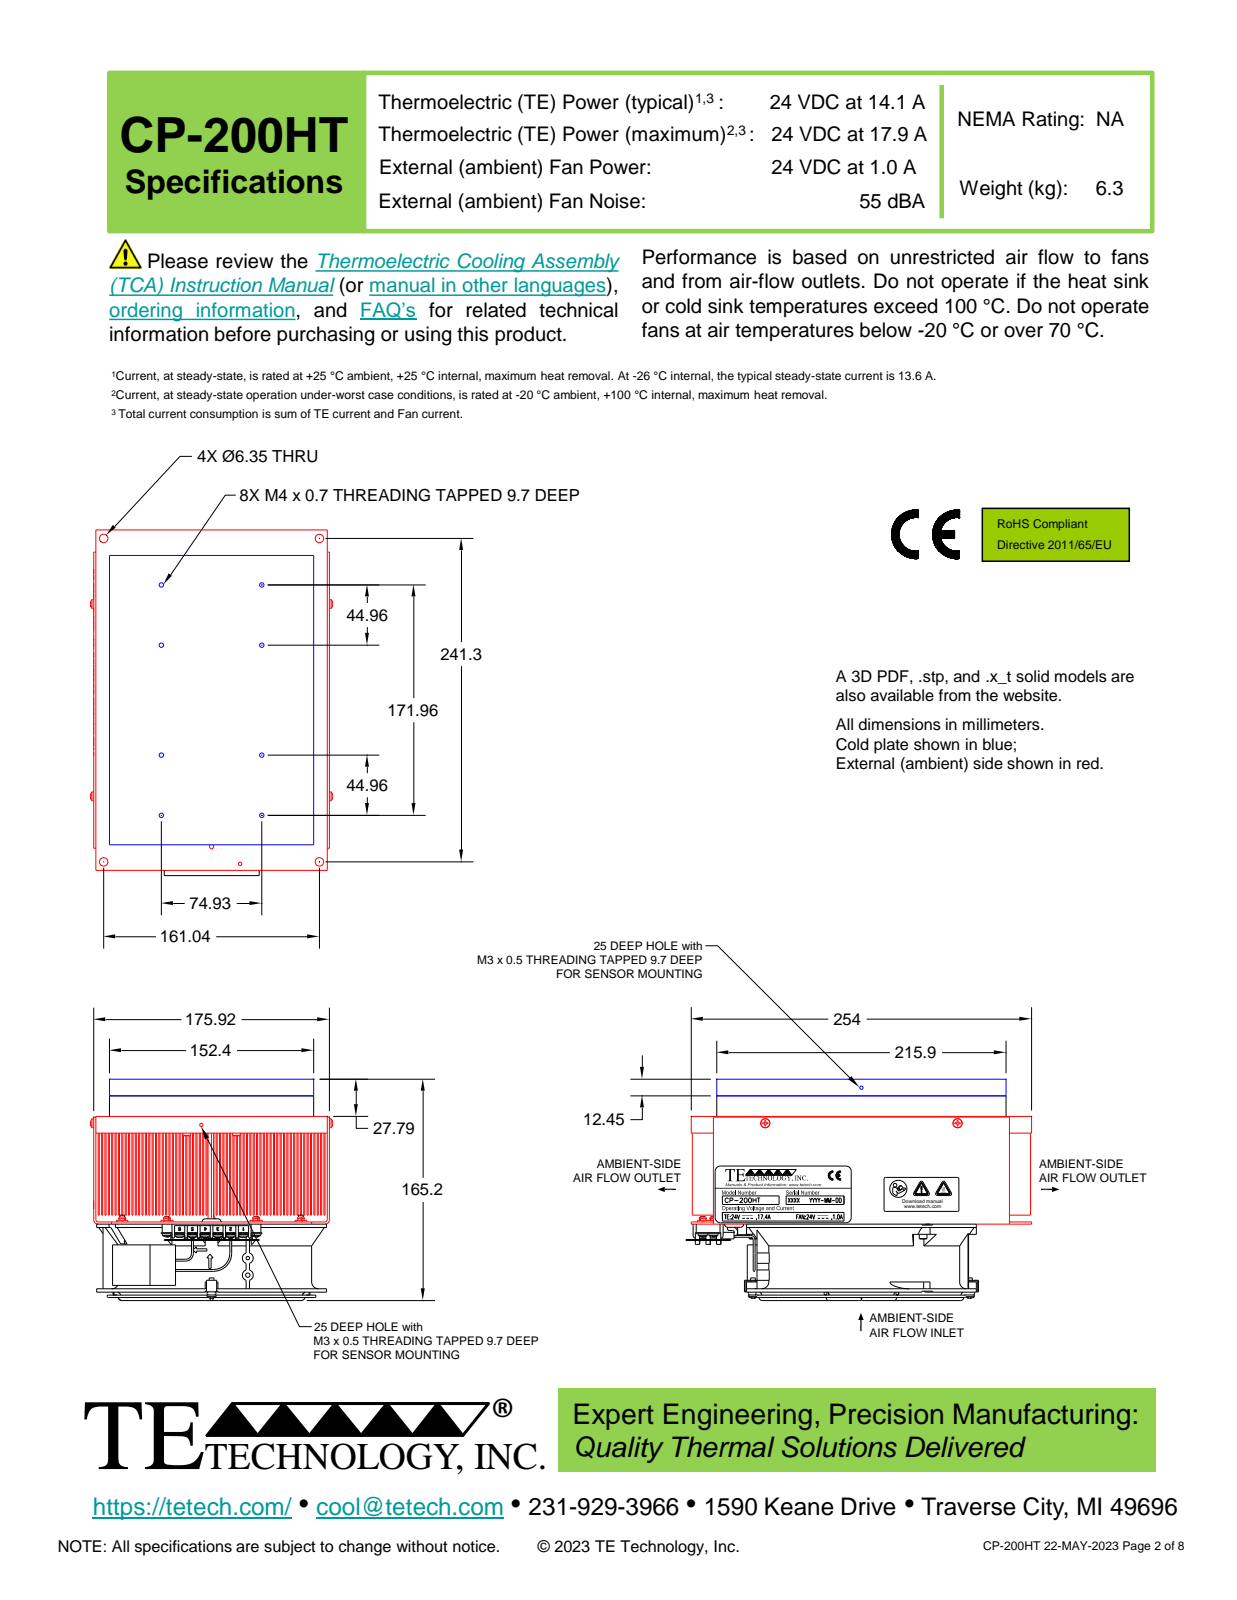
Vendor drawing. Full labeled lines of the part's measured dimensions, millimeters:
Part name (STEP PRODUCT): 7513 module gasket as installed; 825-7521-001 heat sink assy; fan spring clip; 6-32pph x .5 (+8 more)
STEP written by: Alibre (AUTOMOTIVE_DESIGN)
Units: millimetres
Bodies: 169 solids, 3509 faces (2223 planar, 510 cylindrical, 776 other)
Overall size (bounding box): 257.92 × 180.8 × 165.2
Volume: 2 686 000 mm³ · Surface area: 2 450 000 mm²
Round holes (diameter × count): ⌀2.64 ×25, ⌀3.24 ×9, ⌀2.65 ×8, ⌀4.17 ×8, ⌀4.22 ×8, ⌀4.27 ×8, ⌀4.83 ×8, ⌀5.56 ×8, ⌀5.84 ×8, ⌀12.7 ×8, ⌀4.32 ×6, ⌀6.35 ×6
Round bosses / shafts (diameter × count): ⌀3.51 ×30, ⌀6.86 ×20, ⌀2.3 ×16, ⌀5.74 ×11, ⌀9.53 ×9, ⌀10.31 ×8, ⌀6.34 ×8, ⌀6.3 ×8
Partial cylindrical surfaces — rounded edges, fillets, slot ends (radius × count): R0.95 ×21, R0.79 ×16, R0.38 ×8, R0.76 ×8, R0.78 ×8, R0.81 ×8, R1.98 ×8, R1.27 ×5
Main face-to-face distances: 5.03, 2.51, 1.7, 10.06, 7.54, 12.45, 27.79, 12.57, 6.73, 0.81
Hole centre spacings: 7.87, 25.49, 37.08, 51.59, 65.63, 65.84, 75.38, 89.77
